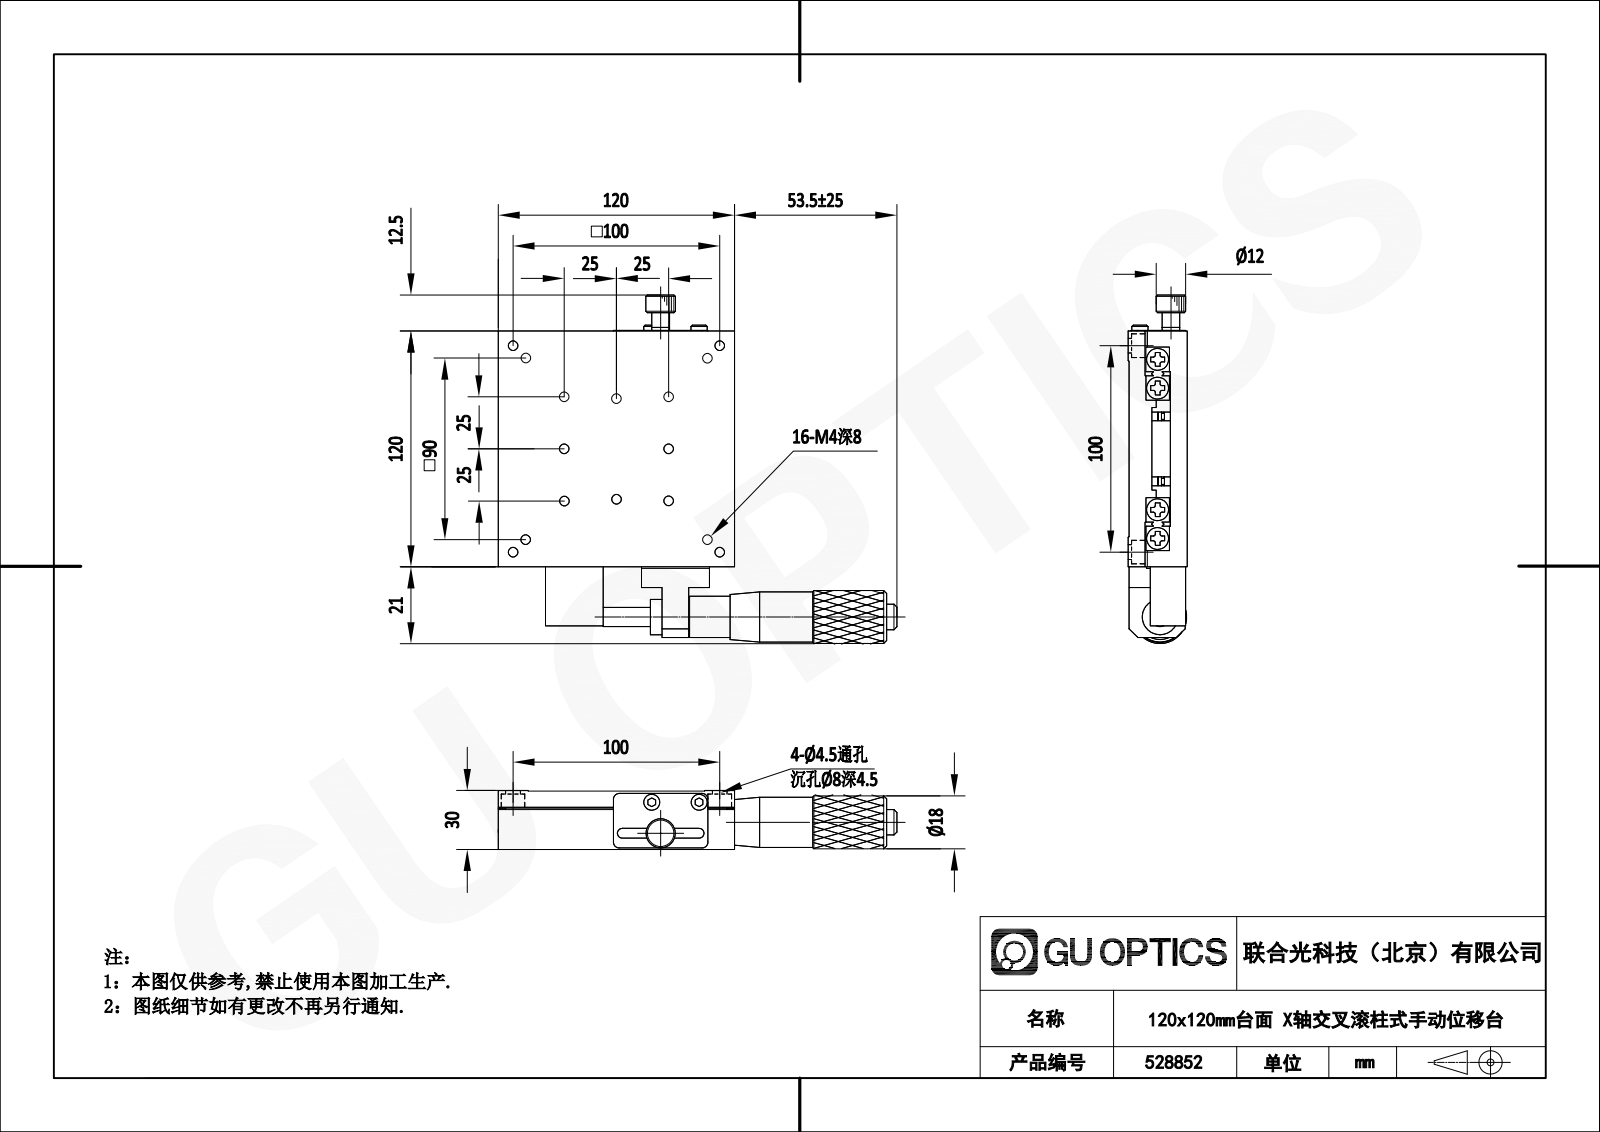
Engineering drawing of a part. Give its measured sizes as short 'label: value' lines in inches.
name: 528852
written by: SolidWorks 2020 (CONFIG_CONTROL_DESIGN)
unit: in
bodies: 3 solids, 2675 faces (283 planar, 650 cylindrical, 1742 other)
size: 6.89 × 6.043 × 1.181
volume: 24.73 in³; area: 159.9 in²
holes: 32× ⌀0.1, 32× ⌀0.173, 24× ⌀0.128, 18× ⌀0.236, 16× ⌀0.062, 16× ⌀0.126, 11× ⌀0.097, 7× ⌀0.097, 6× ⌀0.138, 4× ⌀0.177, 4× ⌀0.315, 1× ⌀0.472
bosses: 4× ⌀0.197, 4× ⌀0.157, 4× ⌀0.098, 1× ⌀0.709, 1× ⌀0.657, 1× ⌀0.5, 1× ⌀0.343, 1× ⌀0.343
rounds: 4× R0.118, 2× R0.071, 1× R0.236, 1× R0.354
face distances: 0.374, 0.512, 0.787, 0.65, 0.276, 1.161, 0.02, 0.039, 0.551, 0.61
hole spacings: 0.591, 1.181, 2.953, 1.772, 0.652, 3.011, 3.282, 1.213
